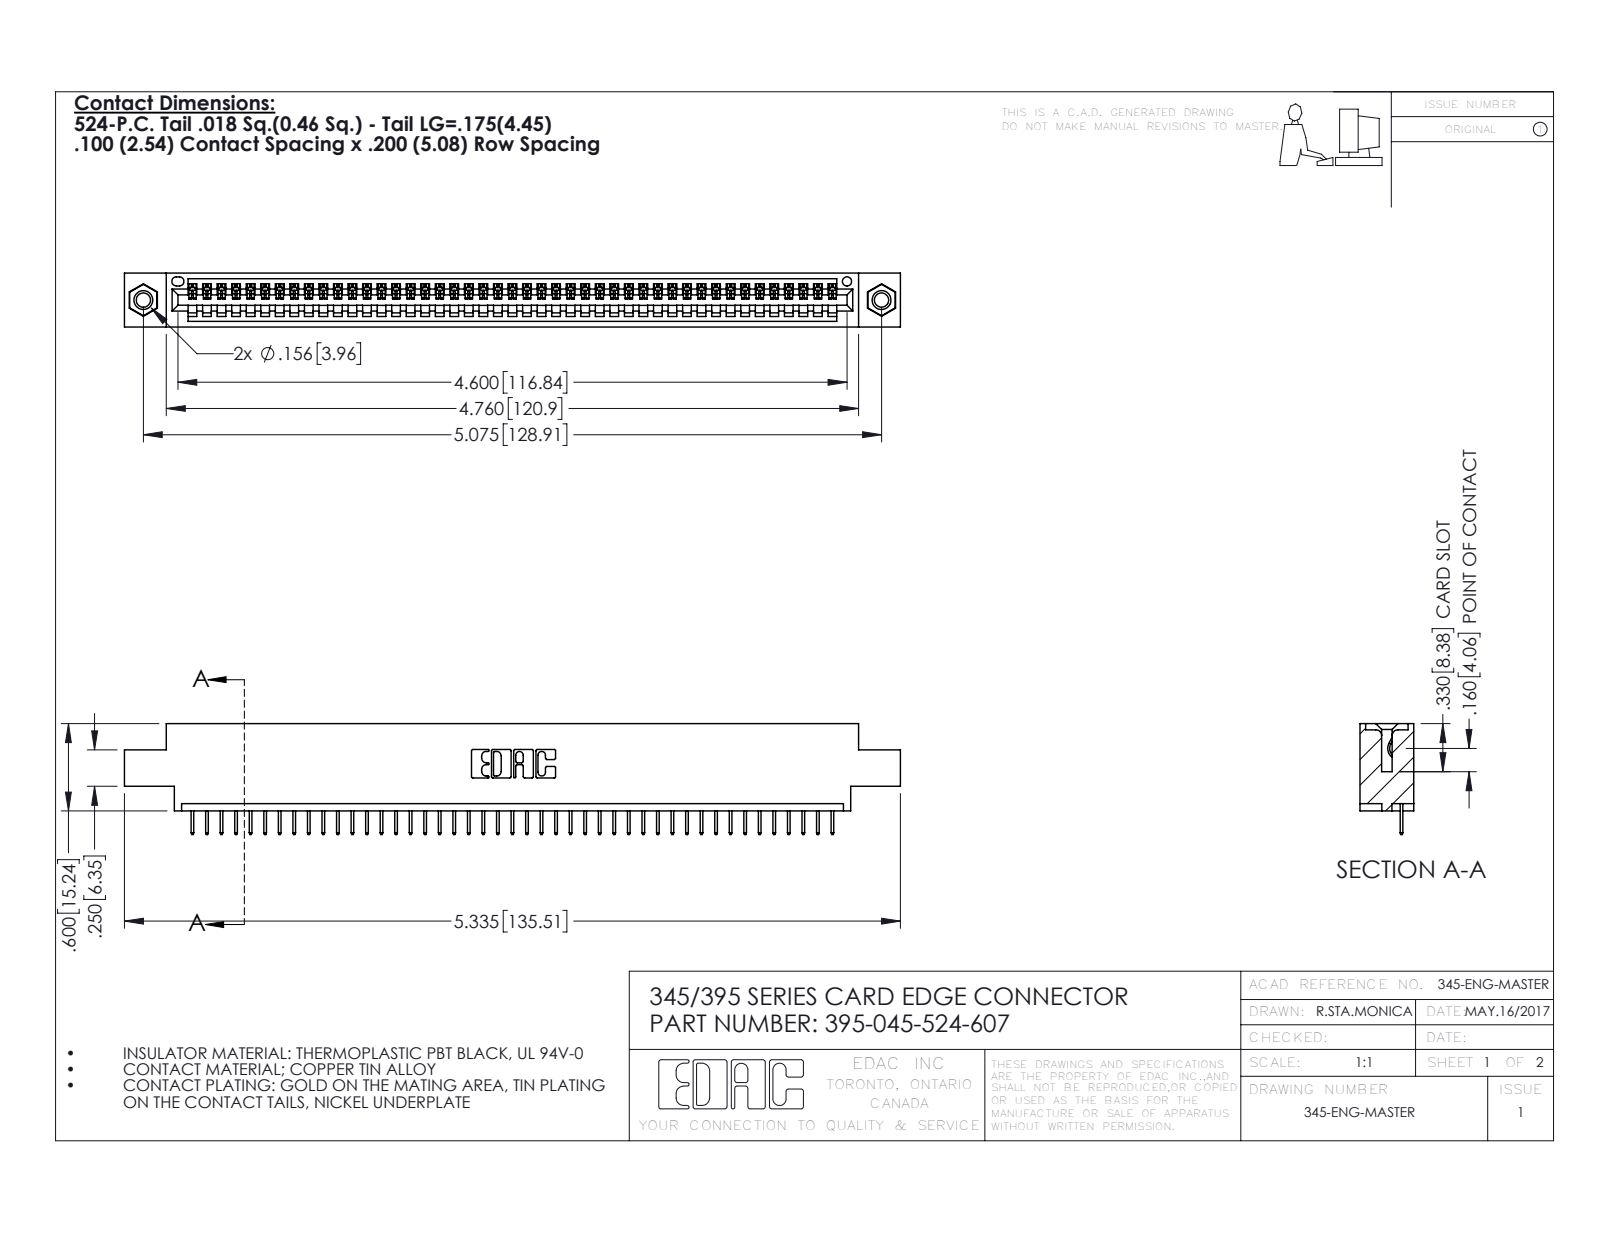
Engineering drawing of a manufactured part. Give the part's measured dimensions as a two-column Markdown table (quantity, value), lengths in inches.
| quantity | value |
| --- | --- |
| part name | 395-045-524-607; 345-250-001_345-250-005-103; 345 Part_0.170 Offset - 0.156 Dia-TI; 345-292-001_345-293-124 |
| STEP written by | SolidWorks 2016 (CONFIG_CONTROL_DESIGN) |
| units | inches |
| bodies | 48 solids, 2980 faces (2186 planar, 778 cylindrical, 16 other) |
| overall size | 5.335 × 0.762 × 0.37 |
| volume | 0.768 in³ |
| surface area | 25.36 in² |
| round holes (diameter × count) | 0.098 × 2, 0.125 × 2, 0.156 × 2, 0.064 × 1 |
| round bosses / shafts (diameter × count) | 0.155 × 2 |
| partial cylindrical surfaces (radius × count) | 0.006 × 90, 0.01 × 22, 0.007 × 6, 0.031 × 6, 0.026 × 3, 0.031 × 2, 0.04 × 2, 0.014 × 1 |
| main face-to-face distances | 0.072, 0.298, 0.37, 0.2, 0.098, 0.272, 0.025, 0.225, 0.072, 0.175 |
| hole center spacings | 0.27, 4.839, 5.075 |
